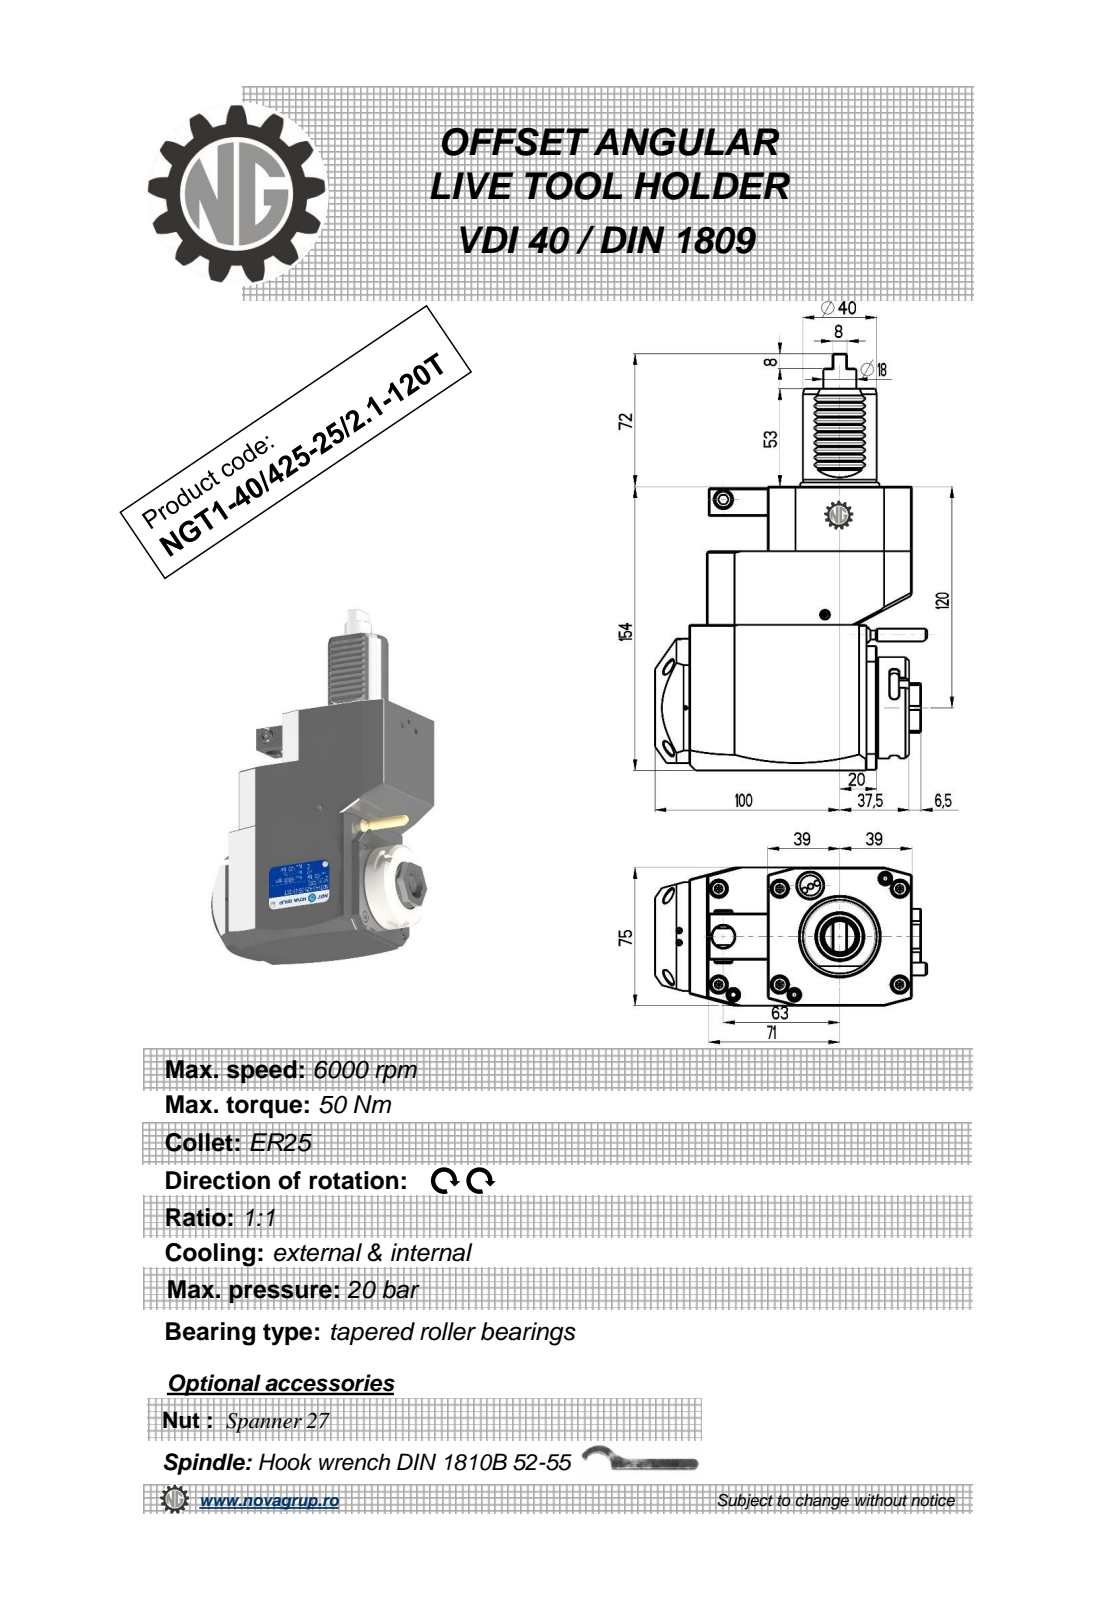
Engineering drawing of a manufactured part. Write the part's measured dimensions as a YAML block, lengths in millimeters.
part_name: "NGT1_40_425_25_1_1_120T"
step_written_by: "PRO/ENGINEER BY PARAMETRIC TECHNOLOGY CORPORATION, 2010280 (CONFIG_CONTROL_DESIGN)"
units: millimeters
bodies: {solids: 1, faces: 327, planar: 189, cylindrical: 70, other: 68}
overall_size: [226, 147.33, 75]
volume: 1260000
surface_area: 87849
round_holes:
  - {diameter: 2.5, count: 1}
  - {diameter: 3, count: 1}
  - {diameter: 9.5, count: 1}
  - {diameter: 12, count: 1}
  - {diameter: 18, count: 1}
round_bosses_or_shafts:
  - {diameter: 8.96, count: 2}
  - {diameter: 55, count: 1}
  - {diameter: 48, count: 1}
  - {diameter: 40, count: 1}
  - {diameter: 17.8, count: 1}
  - {diameter: 10, count: 1}
  - {diameter: 7, count: 1}
  - {diameter: 5, count: 1}
partial_cylinders:
  - {radius: 0.3, count: 10}
  - {radius: 2.5, count: 6}
  - {radius: 0.8, count: 2}
  - {radius: 180, count: 2}
  - {radius: 0.5, count: 1}
  - {radius: 4.25, count: 1}
  - {radius: 15, count: 1}
  - {radius: 24.5, count: 1}
face_to_face_distances: [75, 154, 19, 119, 59, 111, 35, 92, 33, 17.5]
hole_center_spacings: [43.2, 75.07, 112.5]
